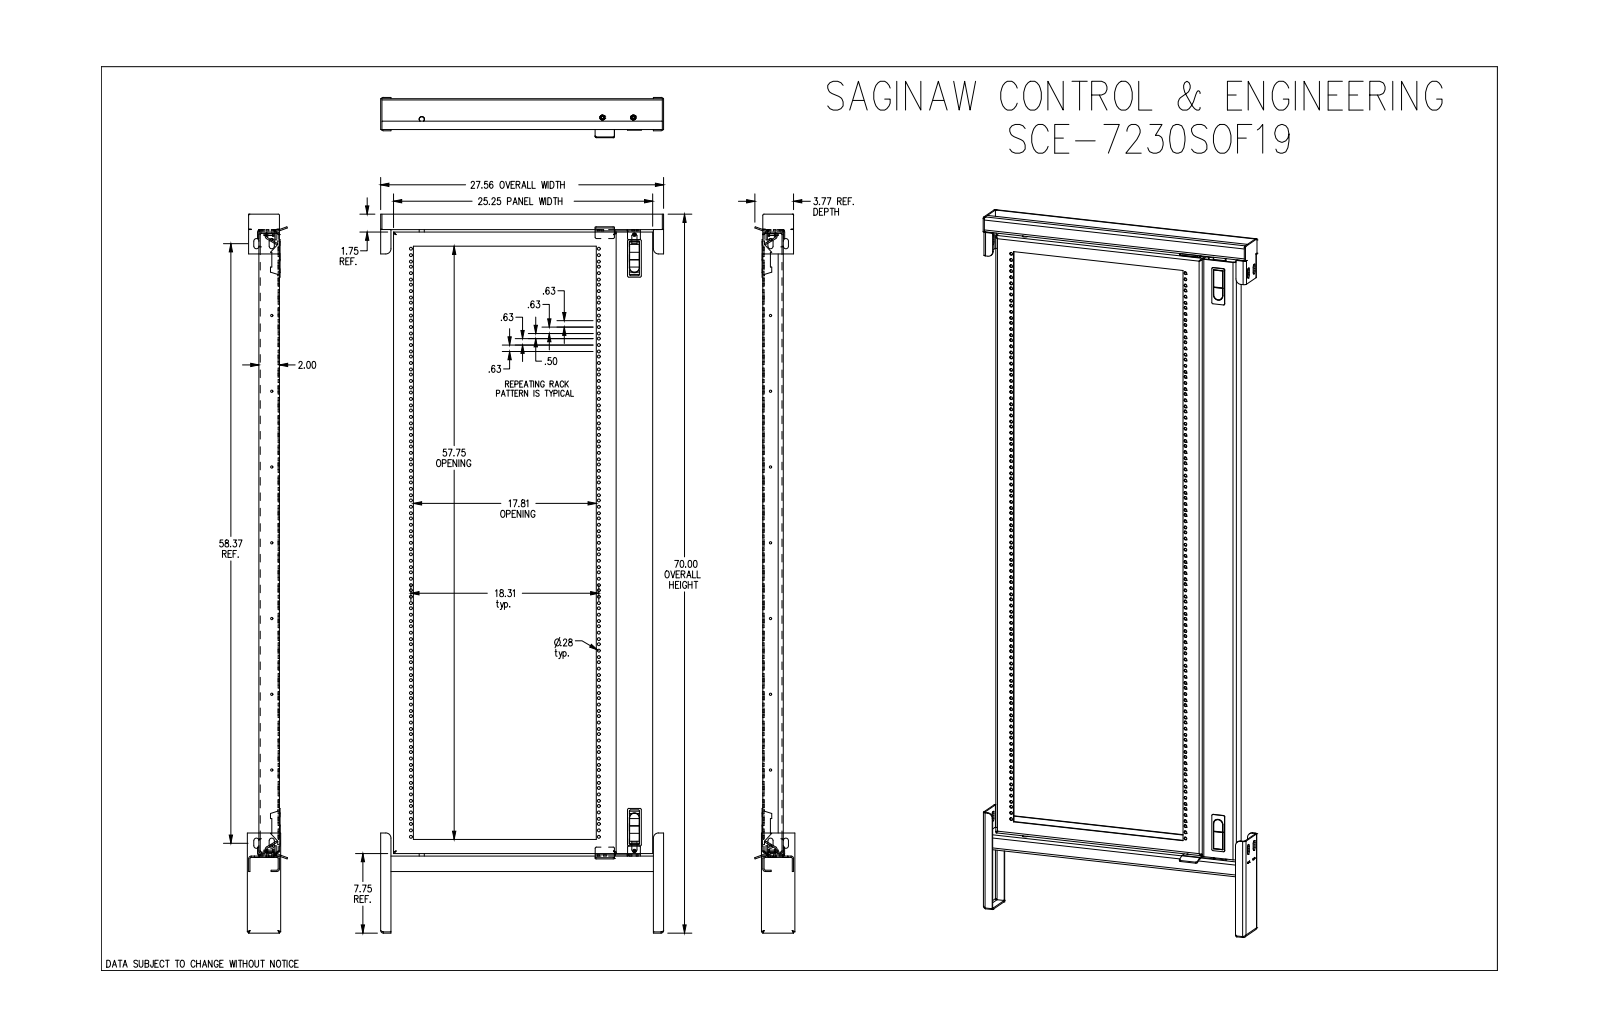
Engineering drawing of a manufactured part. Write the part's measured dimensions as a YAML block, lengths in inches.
part_name: "SCE-7230SOF19"
step_written_by: "SolidWorks 2019 (AUTOMOTIVE_DESIGN)"
units: inches
bodies: {solids: 36, faces: 1705, planar: 1081, cylindrical: 438, other: 186}
overall_size: [69.996, 27.562, 3.92]
volume: 195.5
surface_area: 3228
round_holes:
  - {diameter: 0.281, count: 198}
  - {diameter: 0.19, count: 9}
  - {diameter: 0.193, count: 9}
  - {diameter: 0.25, count: 4}
  - {diameter: 0.313, count: 4}
  - {diameter: 0.187, count: 2}
  - {diameter: 0.187, count: 2}
  - {diameter: 0.503, count: 1}
  - {diameter: 0.531, count: 1}
round_bosses_or_shafts:
  - {diameter: 0.256, count: 9}
  - {diameter: 0.188, count: 9}
  - {diameter: 0.337, count: 4}
  - {diameter: 0.248, count: 4}
  - {diameter: 0.16, count: 2}
  - {diameter: 0.5, count: 1}
partial_cylinders:
  - {radius: 0.125, count: 52}
  - {radius: 0.25, count: 44}
  - {radius: 0.125, count: 14}
  - {radius: 0.031, count: 12}
  - {radius: 0.062, count: 9}
  - {radius: 0.02, count: 4}
  - {radius: 0.15, count: 4}
  - {radius: 0.5, count: 4}
face_to_face_distances: [0.125, 0.125, 1.874, 21.563, 2.875, 0.25, 3.437, 61.118, 2, 1.875]
hole_center_spacings: [1.75, 3.5, 5.25, 7, 8.75, 10.5, 0.625, 0.625]
